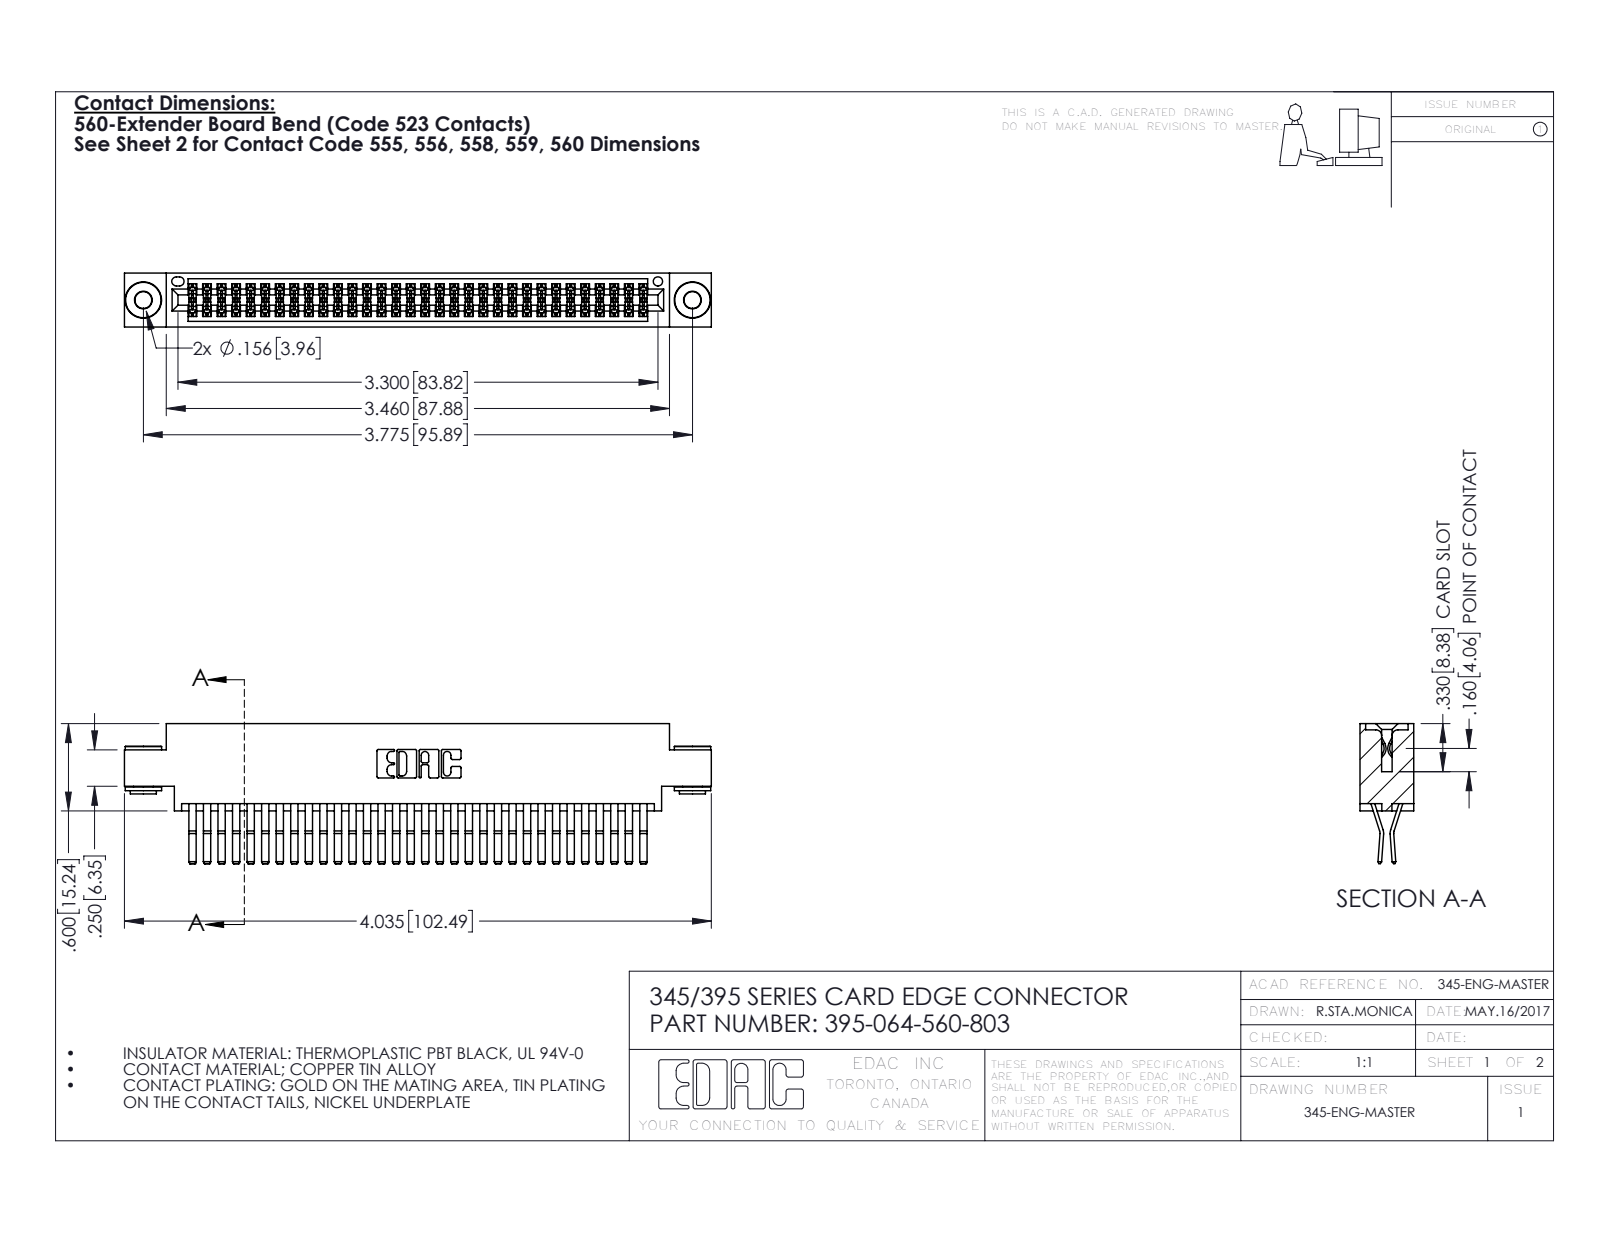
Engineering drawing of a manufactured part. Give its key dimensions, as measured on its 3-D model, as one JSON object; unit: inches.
{"part_name": "395-064-560-803; 345-292-001_560 Tail; 345-250-002_345-250-002-102; 345 Part_0.170 Offset - 0.156 Dia-TH", "step_written_by": "SolidWorks 2016 (CONFIG_CONTROL_DESIGN)", "units": "inches", "bodies": {"solids": 67, "faces": 3496, "planar": 2206, "cylindrical": 1282, "other": 8}, "overall_size": [4.035, 0.962, 0.37], "volume_in3": 0.622, "surface_area_in2": 25.26, "round_holes": [[0.116, 2], [0.156, 2], [0.064, 1]], "round_bosses_or_shafts": [[0.25, 2], [0.18, 2], [0.136, 2]], "partial_cylinders_radius": [[0.006, 97], [0.01, 22], [0.007, 6], [0.031, 6], [0.026, 3], [0.01, 2], [0.014, 2], [0.019, 2]], "face_to_face_distances": [0.025, 0.072, 0.298, 0.37, 0.2, 0.098, 0.272, 0.225, 0.175, 0.149], "hole_center_spacings": [0.27, 3.54, 3.775]}
